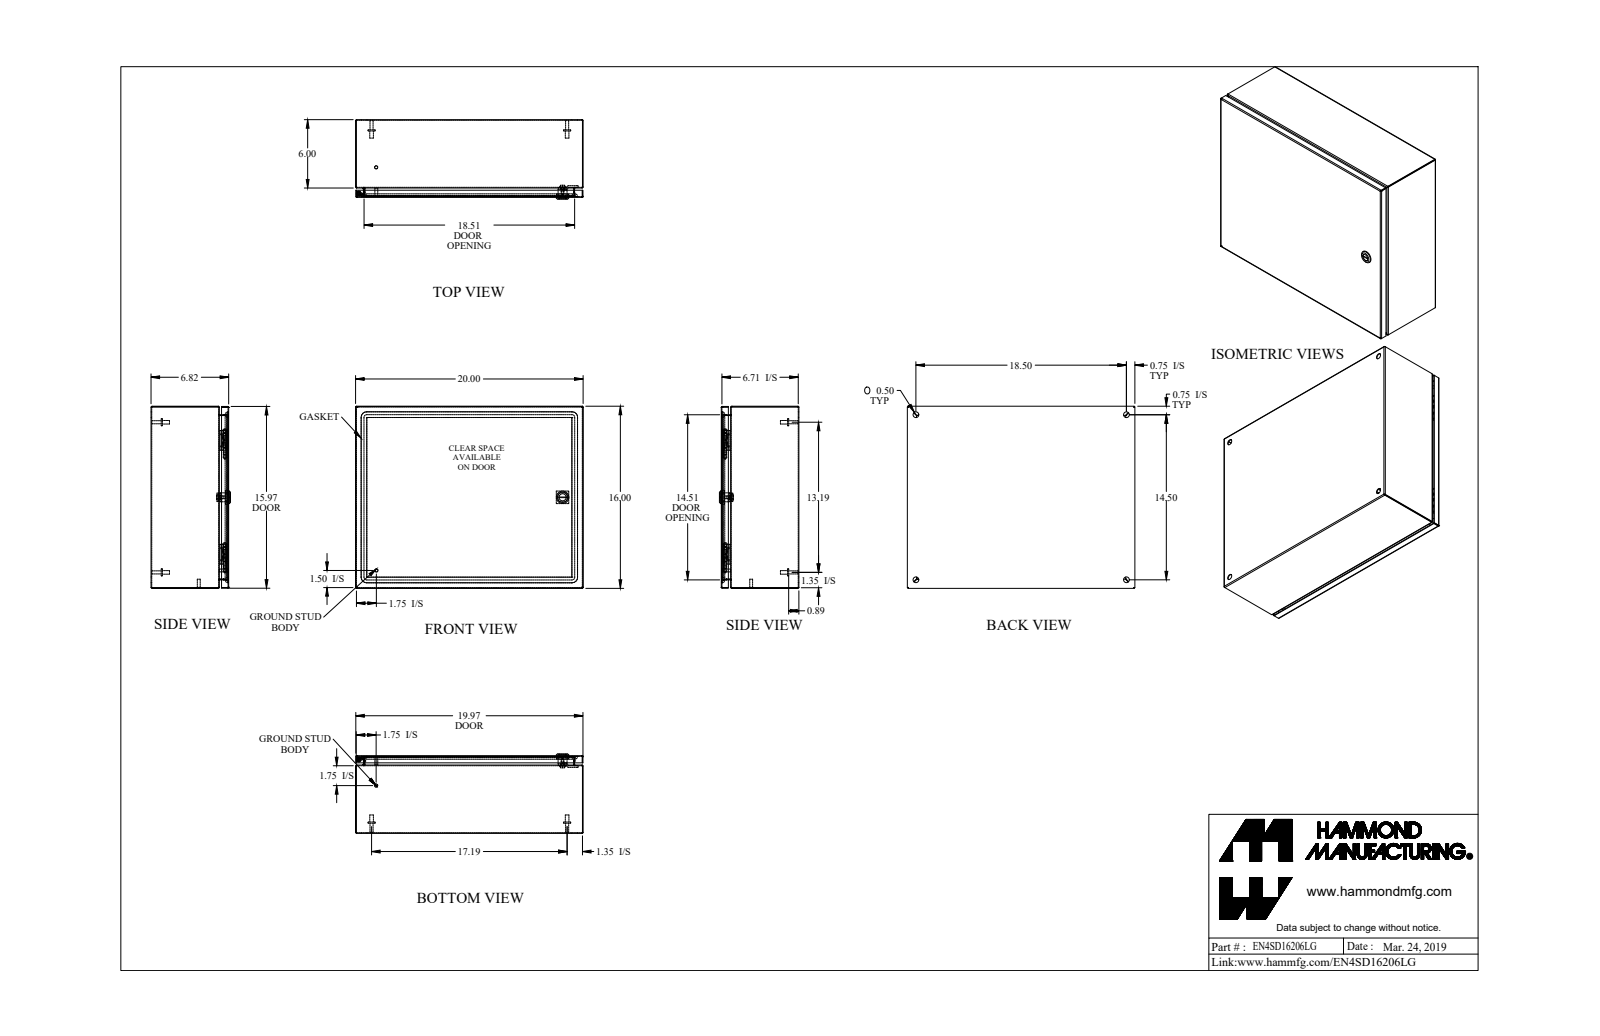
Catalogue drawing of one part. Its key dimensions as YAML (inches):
part_name: "EN4SD16206LG_Default"
step_written_by: "SolidWorks 2019 (CONFIG_CONTROL_DESIGN)"
units: inches
bodies: {solids: 21, faces: 634, planar: 285, cylindrical: 213, other: 136}
overall_size: [20, 16, 6.982]
volume: 76.29
surface_area: 2585
round_holes:
  - {diameter: 0.5, count: 4}
  - {diameter: 0.172, count: 1}
  - {diameter: 0.232, count: 1}
  - {diameter: 0.24, count: 1}
  - {diameter: 0.242, count: 1}
  - {diameter: 0.625, count: 1}
  - {diameter: 0.785, count: 1}
round_bosses_or_shafts:
  - {diameter: 0.625, count: 4}
  - {diameter: 0.313, count: 4}
  - {diameter: 0.27, count: 4}
  - {diameter: 0.281, count: 2}
  - {diameter: 0.25, count: 2}
  - {diameter: 1.1, count: 1}
  - {diameter: 0.525, count: 1}
  - {diameter: 0.455, count: 1}
partial_cylinders:
  - {radius: 0.029, count: 21}
  - {radius: 0.086, count: 21}
  - {radius: 0.25, count: 16}
  - {radius: 19, count: 8}
  - {radius: 0.006, count: 4}
  - {radius: 0.062, count: 4}
  - {radius: 0.499, count: 4}
  - {radius: 0.125, count: 2}
face_to_face_distances: [0.057, 6.765, 6.708, 6.822, 15.943, 19.943, 15.886, 16, 19.886, 20]
hole_center_spacings: [14.5, 18.5, 18.888, 23.506, 7.326, 7.327]
